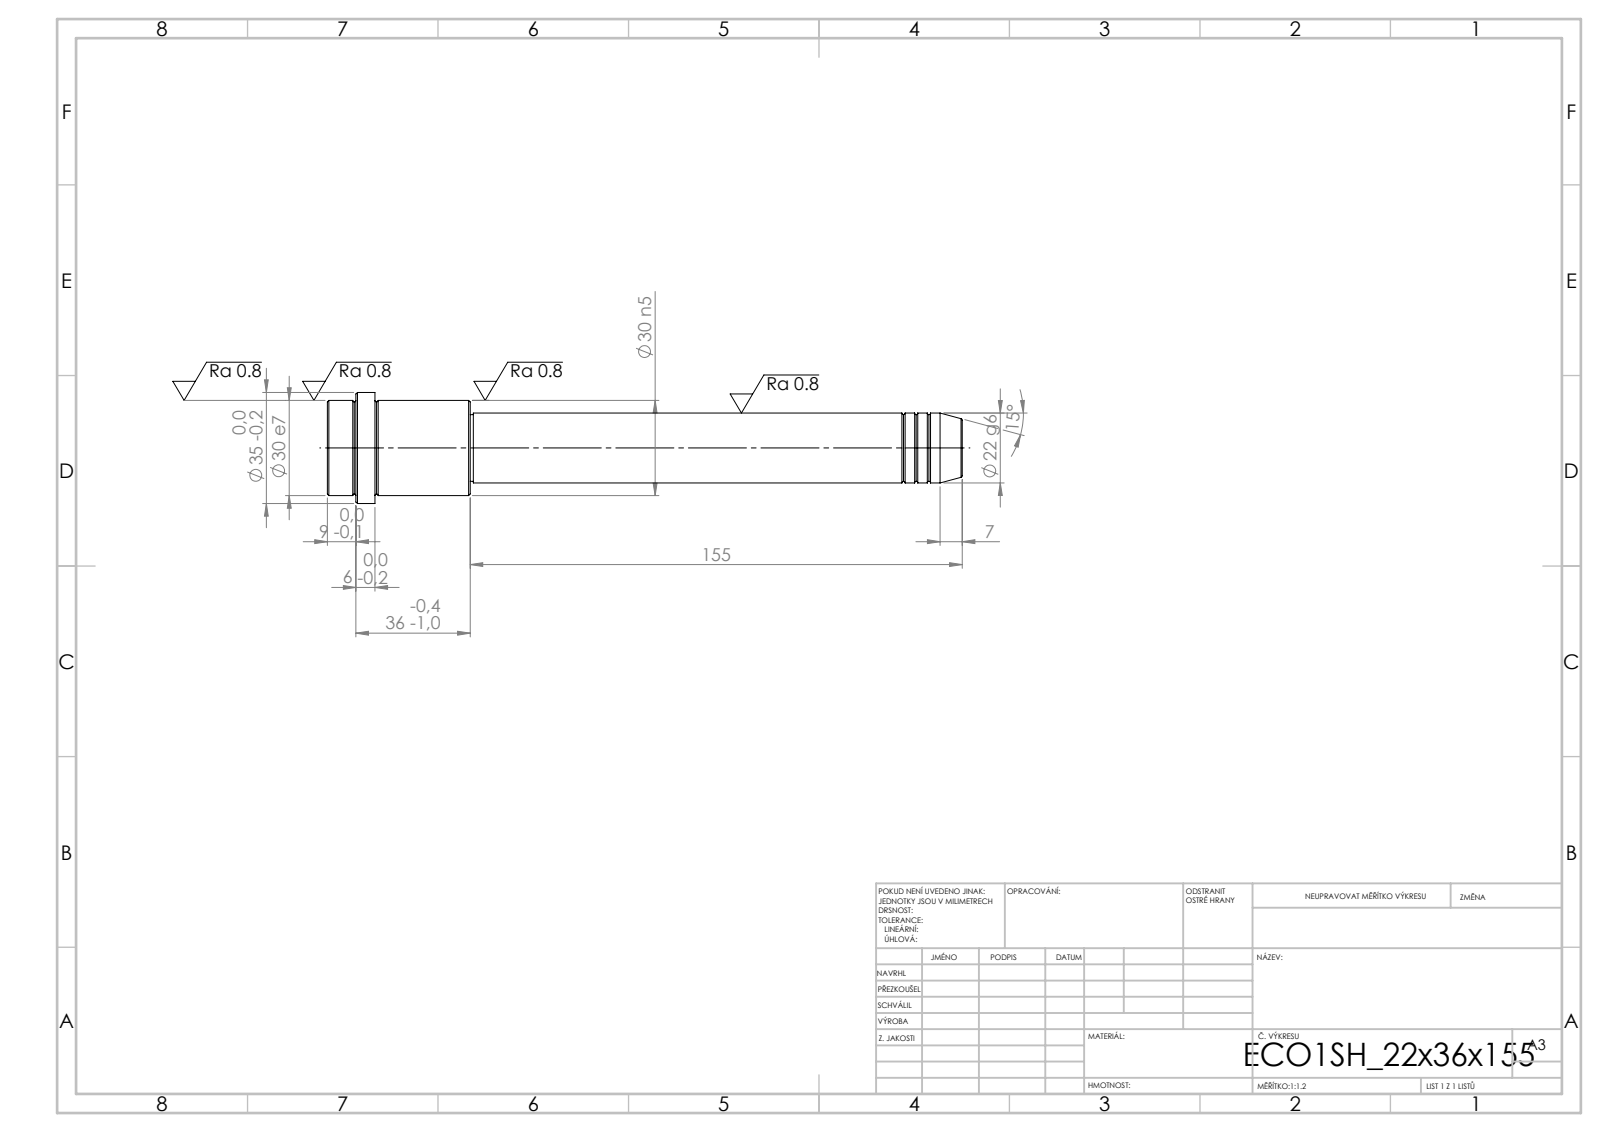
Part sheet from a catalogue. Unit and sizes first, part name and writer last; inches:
Units: inches
Overall size (bounding box): 7.874 × 1.378 × 1.378
Round bosses / shafts (diameter × count): ⌀1.378 ×1, ⌀1.181 ×1, ⌀0.866 ×1, ⌀0.827 ×1
Main face-to-face distances: 1.772, 1.181, 0.591, 6.102, 7.283, 7.874, 7.52, 1.417, 0.236, 0.354
Volume: 5.59 in³ · Surface area: 26.36 in²
Bodies: 1 solid, 52 faces (6 planar, 16 cylindrical, 30 other)
STEP written by: SolidWorks 2019 (CONFIG_CONTROL_DESIGN)
